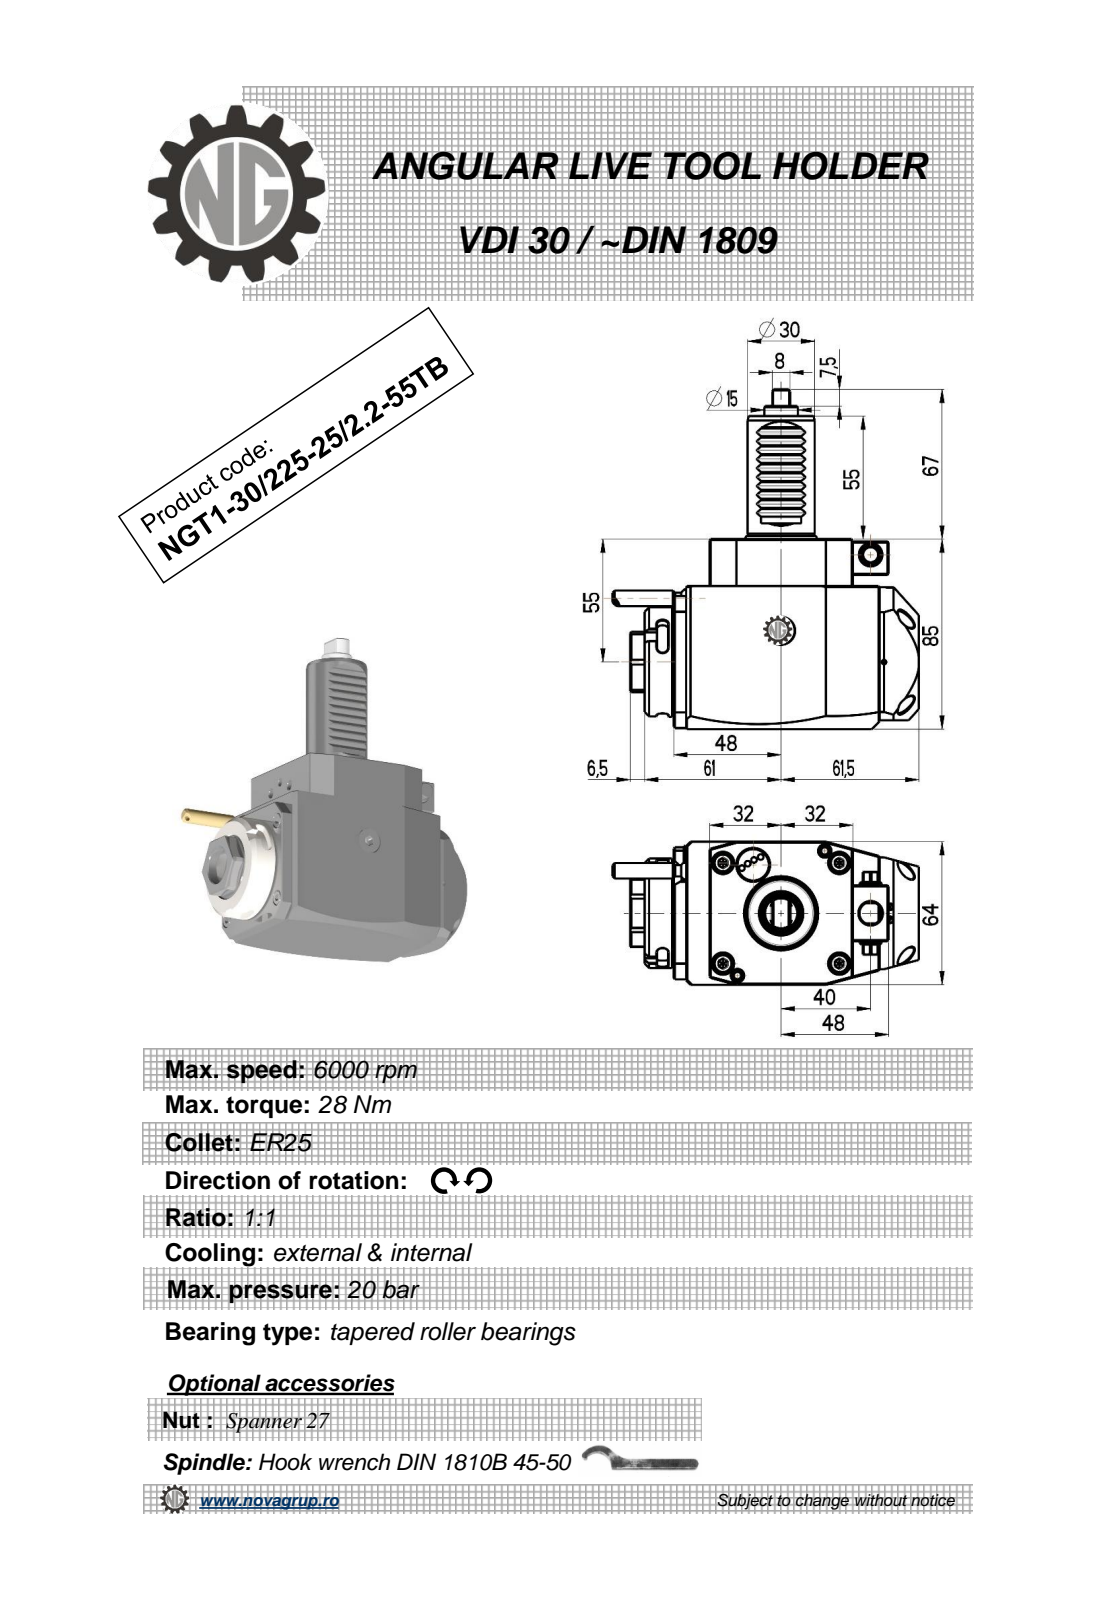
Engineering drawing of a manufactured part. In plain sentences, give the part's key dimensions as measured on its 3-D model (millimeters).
The part is named "NGT1_30_225_25_1_2_55TB". Its 3-D file was written by "PRO/ENGINEER BY PARAMETRIC TECHNOLOGY CORPORATION, 2010280 (CONFIG_CONTROL_DESIGN)". It is 1 solid with 352 faces: 192 planar, 88 cylindrical and 72 other. Overall it measures 152 by 136.88 by 64 millimeters. Its volume is 555 062 cubic millimeters and its surface area 49 998 square millimeters. Round holes: 1 of diameter 2.5, 1 of diameter 3, 1 of diameter 9.5, 1 of diameter 10, 1 of diameter 18. Round bosses or shafts: 2 of diameter 8, 1 of diameter 49, 1 of diameter 42, 1 of diameter 30, 1 of diameter 15, 1 of diameter 10, 1 of diameter 7, 1 of diameter 5. Partial cylindrical surfaces (rounded edges, fillets, slot ends): 10 of radius 0.3, 6 of radius 2.5, 2 of radius 0.8, 2 of radius 180, 1 of radius 3.85, 1 of radius 4.25, 1 of radius 4.5, 1 of radius 7.2. The main face-to-face distances are 64, 85, 16, 80, 109.5, 13, 21, 122.5, 29, 93.5. The hole center spacings are 26.17, 34.25, 46.5.
